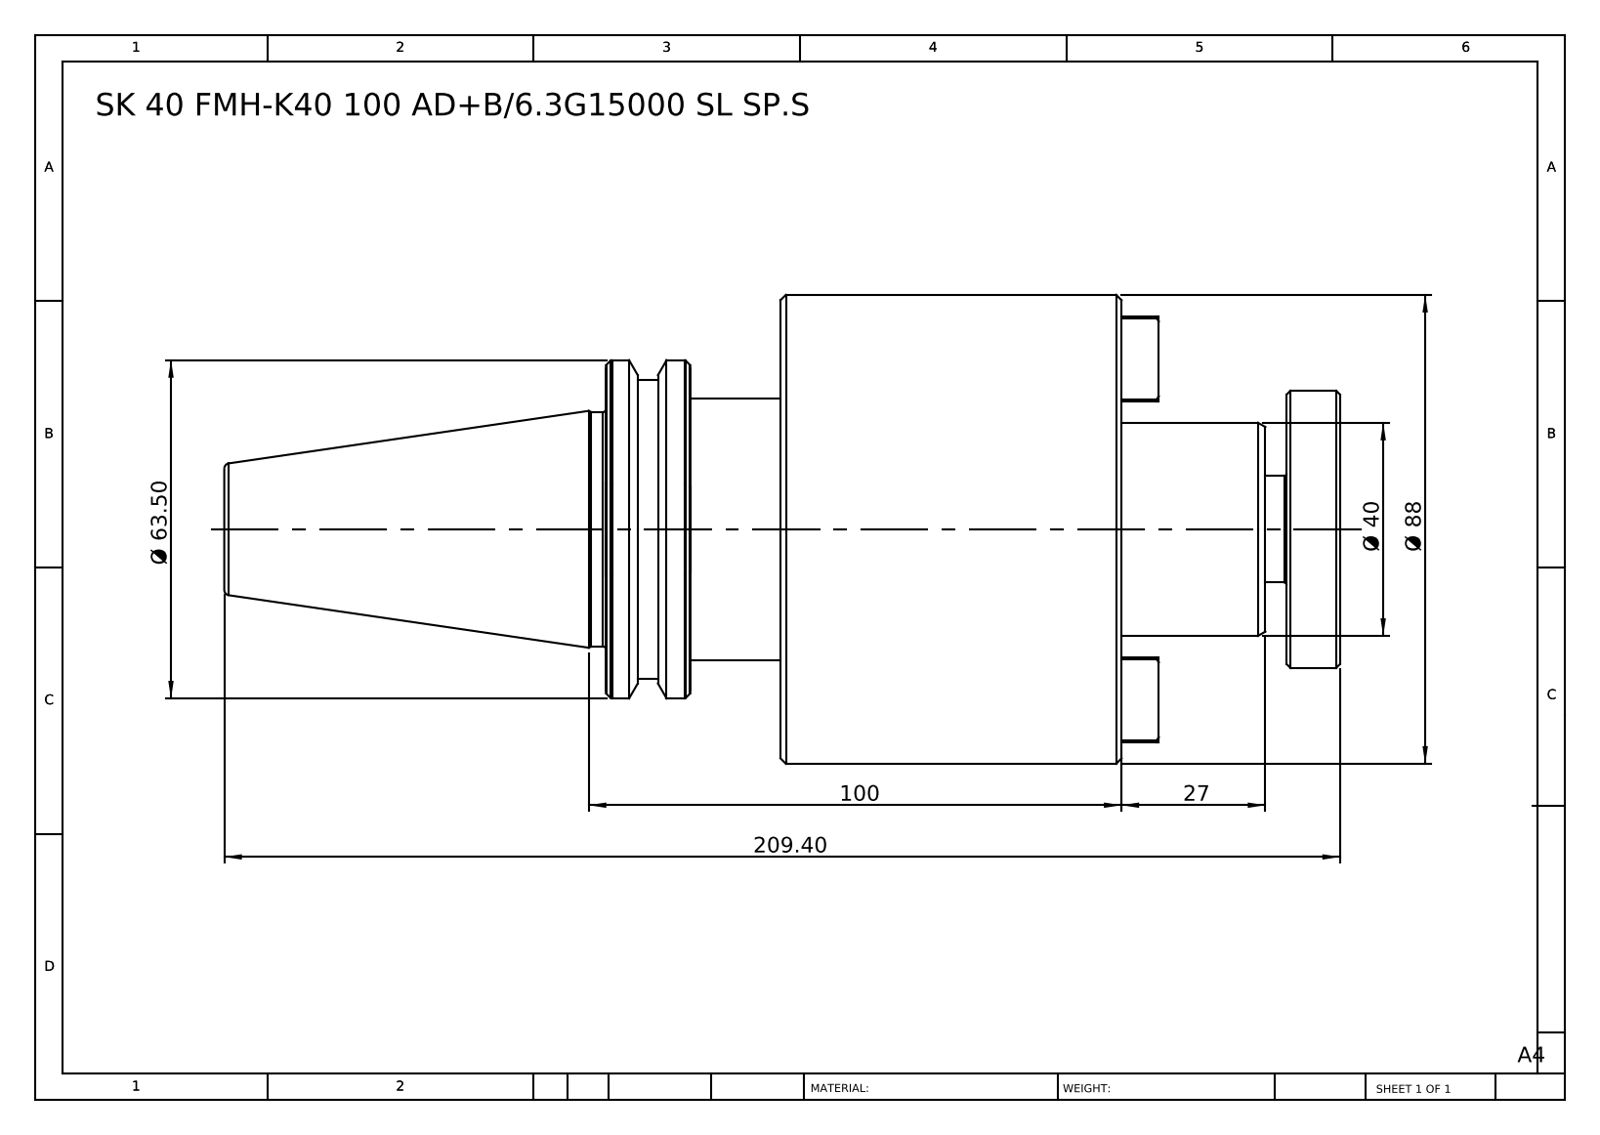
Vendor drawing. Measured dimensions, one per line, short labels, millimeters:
name: SK40 FMH40 120 AD-6.3G15000 SL SP.S
written by: SolidWorks 2014 (CONFIG_CONTROL_DESIGN)
unit: mm
bodies: 1 solid, 110 faces (36 planar, 18 cylindrical, 56 other)
size: 209.4 × 88 × 88
volume: 597 821 mm³; area: 54 841 mm²
bosses: 1× ⌀88, 1× ⌀63.5, 1× ⌀56, 1× ⌀52, 1× ⌀49, 1× ⌀44, 1× ⌀40, 1× ⌀20
face distances: 64, 41, 105, 10, 31, 95, 137.8, 127.8, 96.8, 32.8
